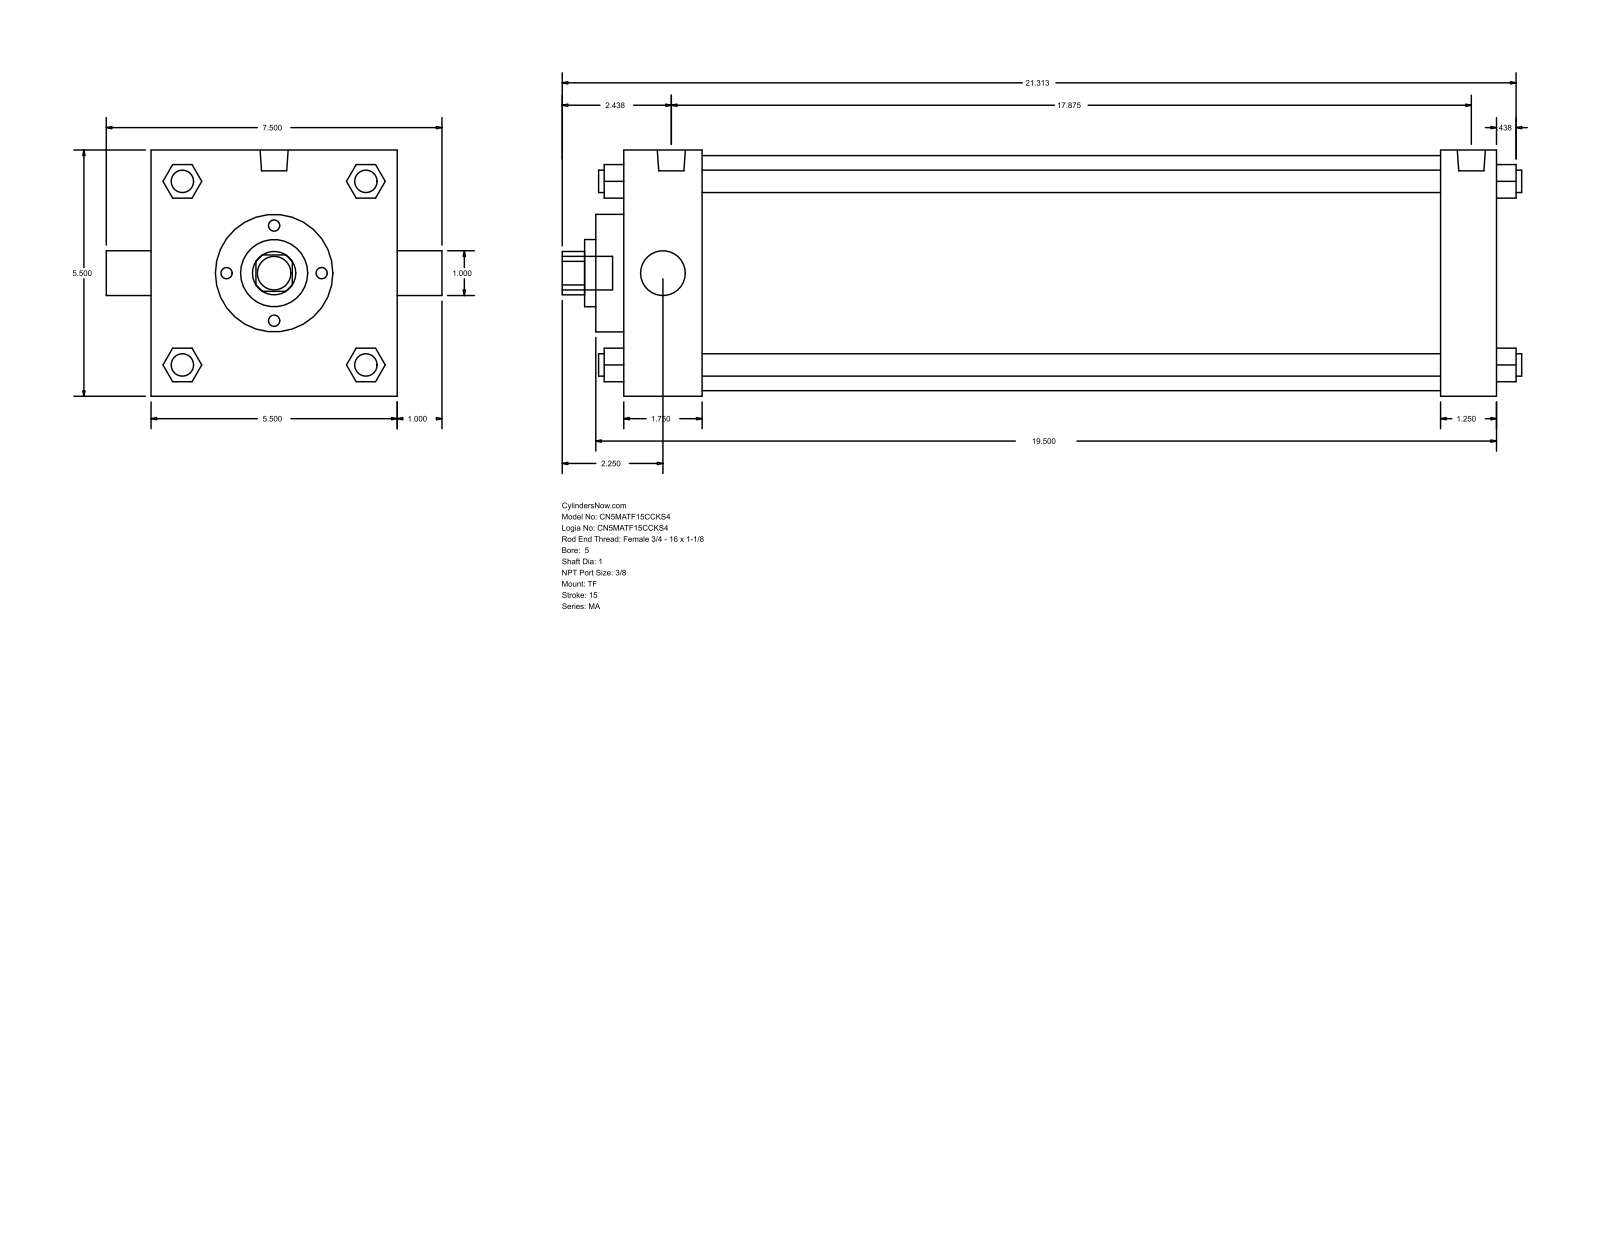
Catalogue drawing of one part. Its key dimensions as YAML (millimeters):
part_name: "MA_TF__0500_1"
step_written_by: "GSSL Pune (CONFIG_CONTROL_DESIGN)"
units: millimeters
bodies: {solids: 0, faces: 122, planar: 93, cylindrical: 29, other: 0}
overall_size: [544.51, 190.5, 139.7]
round_holes:
  - {diameter: 25.4, count: 2}
  - {diameter: 38.1, count: 1}
  - {diameter: 66.67, count: 1}
  - {diameter: 133.35, count: 1}
round_bosses_or_shafts:
  - {diameter: 12.7, count: 4}
  - {diameter: 11.11, count: 3}
  - {diameter: 15.93, count: 2}
  - {diameter: 19.05, count: 1}
partial_cylinders:
  - {radius: 12.29, count: 1}
face_to_face_distances: [139.7, 495.31, 463.56, 31.75, 44.46, 419.1, 450.85, 15.87, 60.33, 479.43]
